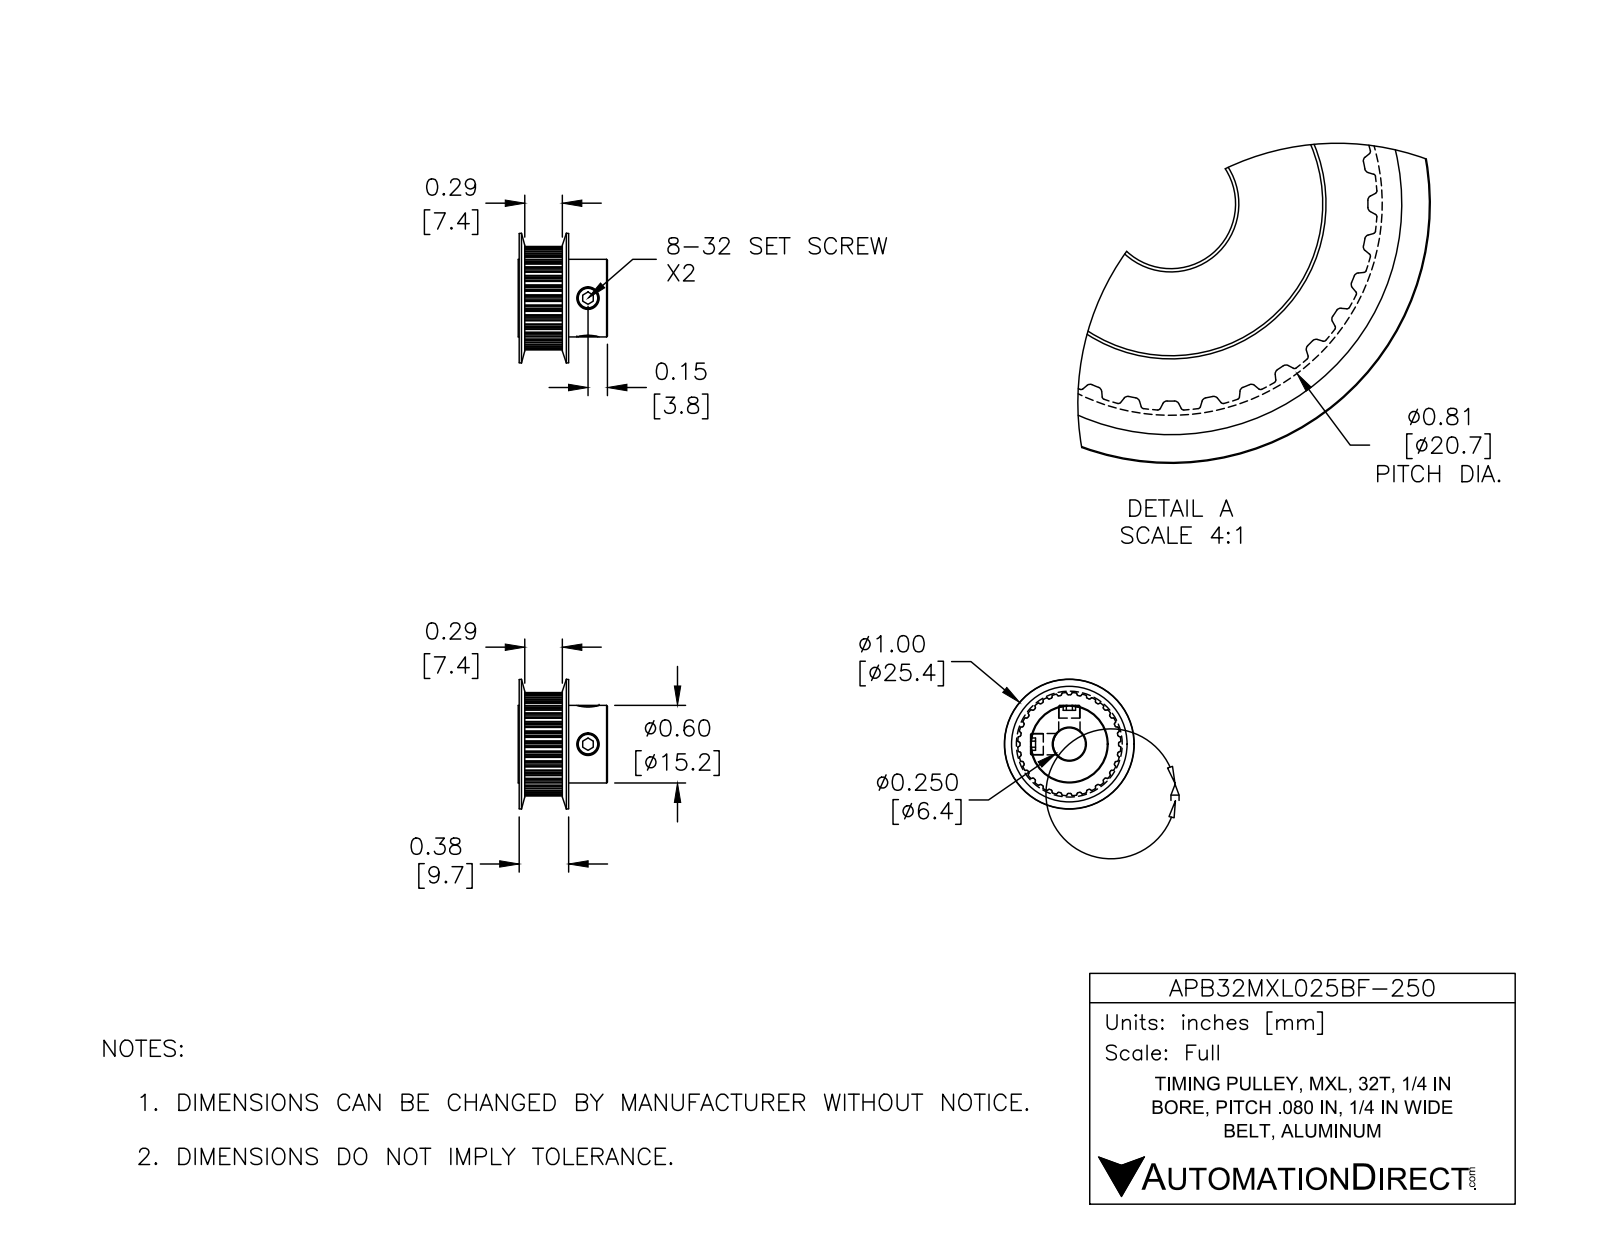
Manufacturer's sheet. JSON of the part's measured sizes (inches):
{"part_name": "APB32MXL025BF-250", "step_written_by": "SolidWorks 2016 (AUTOMOTIVE_DESIGN)", "units": "inches", "bodies": {"solids": 3, "faces": 345, "planar": 88, "cylindrical": 231, "other": 26}, "overall_size": [1, 1, 0.688], "volume_in3": 0.236, "surface_area_in2": 4.583, "round_holes": [[0.164, 2], [0.25, 1]], "round_bosses_or_shafts": [[0.16, 2], [0.598, 1]], "partial_cylinders_radius": [[0.005, 64], [0.009, 64], [0.38, 1], [0.398, 1]], "face_to_face_distances": [0.346, 0.025, 0.37, 0.687, 0.663, 0.317, 0.335, 0.34, 0.315, 0.031]}
